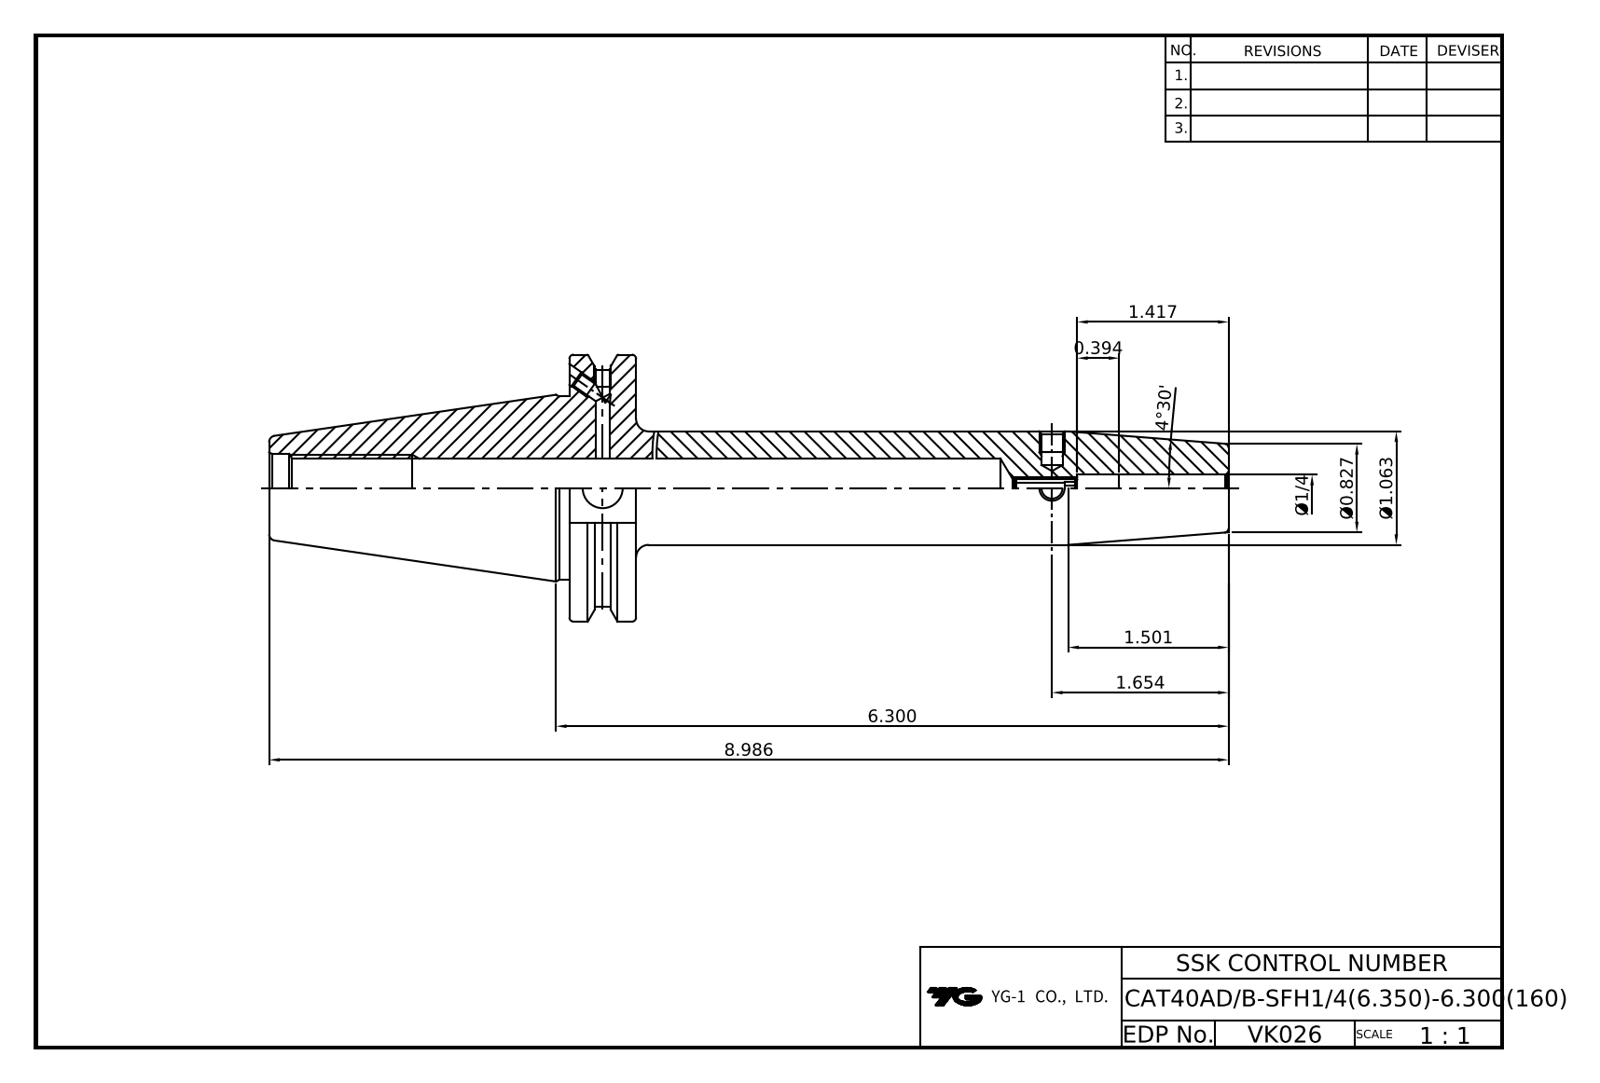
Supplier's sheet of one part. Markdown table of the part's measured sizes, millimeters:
| quantity | value |
| --- | --- |
| part name | LO-CAT40ADB-SFH6.35-160 |
| STEP written by | Autodesk Inventor 2022 (AUTOMOTIVE_DESIGN) |
| units | millimeters |
| bodies | 1 solid, 87 faces (37 planar, 29 cylindrical, 21 other) |
| overall size | 228.25 × 63.5 × 61.09 |
| volume | 163 970 mm³ |
| surface area | 36 679 mm² |
| round holes (diameter × count) | 3.24 × 4, 4 × 2, 4.2 × 2, 4.3 × 1, 6.35 × 1, 7.55 × 1, 9.53 × 1, 13 × 1, 13.39 × 1, 16.3 × 1 |
| round bosses / shafts (diameter × count) | 63.5 × 1, 43.6 × 1, 27 × 1 |
| partial cylindrical surfaces (radius × count) | 28.15 × 1 |
| main face-to-face distances | 15.88, 156.83, 140.95, 47.6, 16.38, 71.42, 87.3, 228.25, 77.47, 6.05 |
